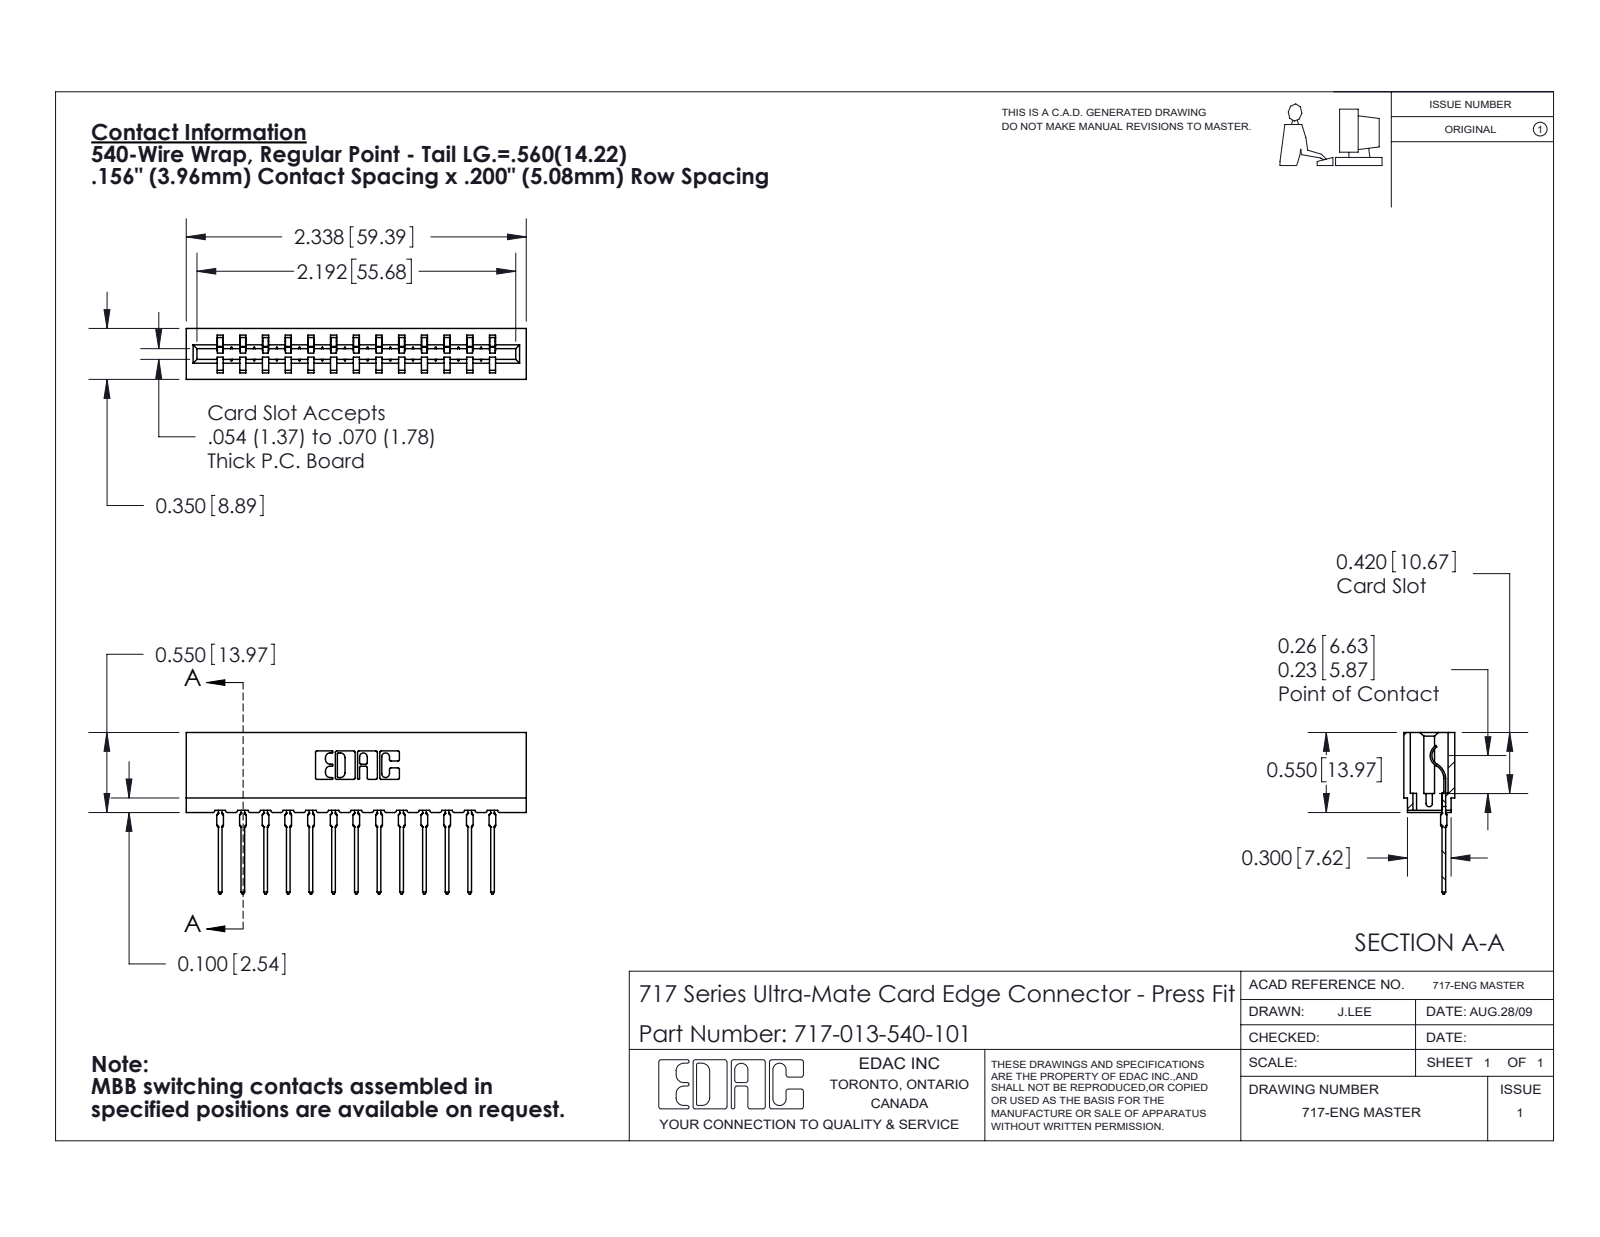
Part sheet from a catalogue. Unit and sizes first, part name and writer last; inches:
Units: inches
Overall size (bounding box): 2.338 × 1.109 × 0.35
Partial cylindrical surfaces — rounded edges, fillets, slot ends (radius × count): R0.015 ×26, R0.021 ×26, R0.01 ×22, R0.007 ×6, R0.031 ×6, R0.005 ×4, R0.011 ×4, R0.026 ×3
Main face-to-face distances: 0.212, 0.138, 0.156, 0.35, 0.624, 0.468, 0.312, 0.198, 0.074, 0.042
Volume: 0.316 in³ · Surface area: 11.01 in²
Bodies: 14 solids, 1563 faces (938 planar, 287 cylindrical, 338 other)
Part name (STEP PRODUCT): 717-013-540-101; 745-292-001_540; 717 Part_Insulator Option - 06
STEP written by: SolidWorks 2020 (CONFIG_CONTROL_DESIGN)
